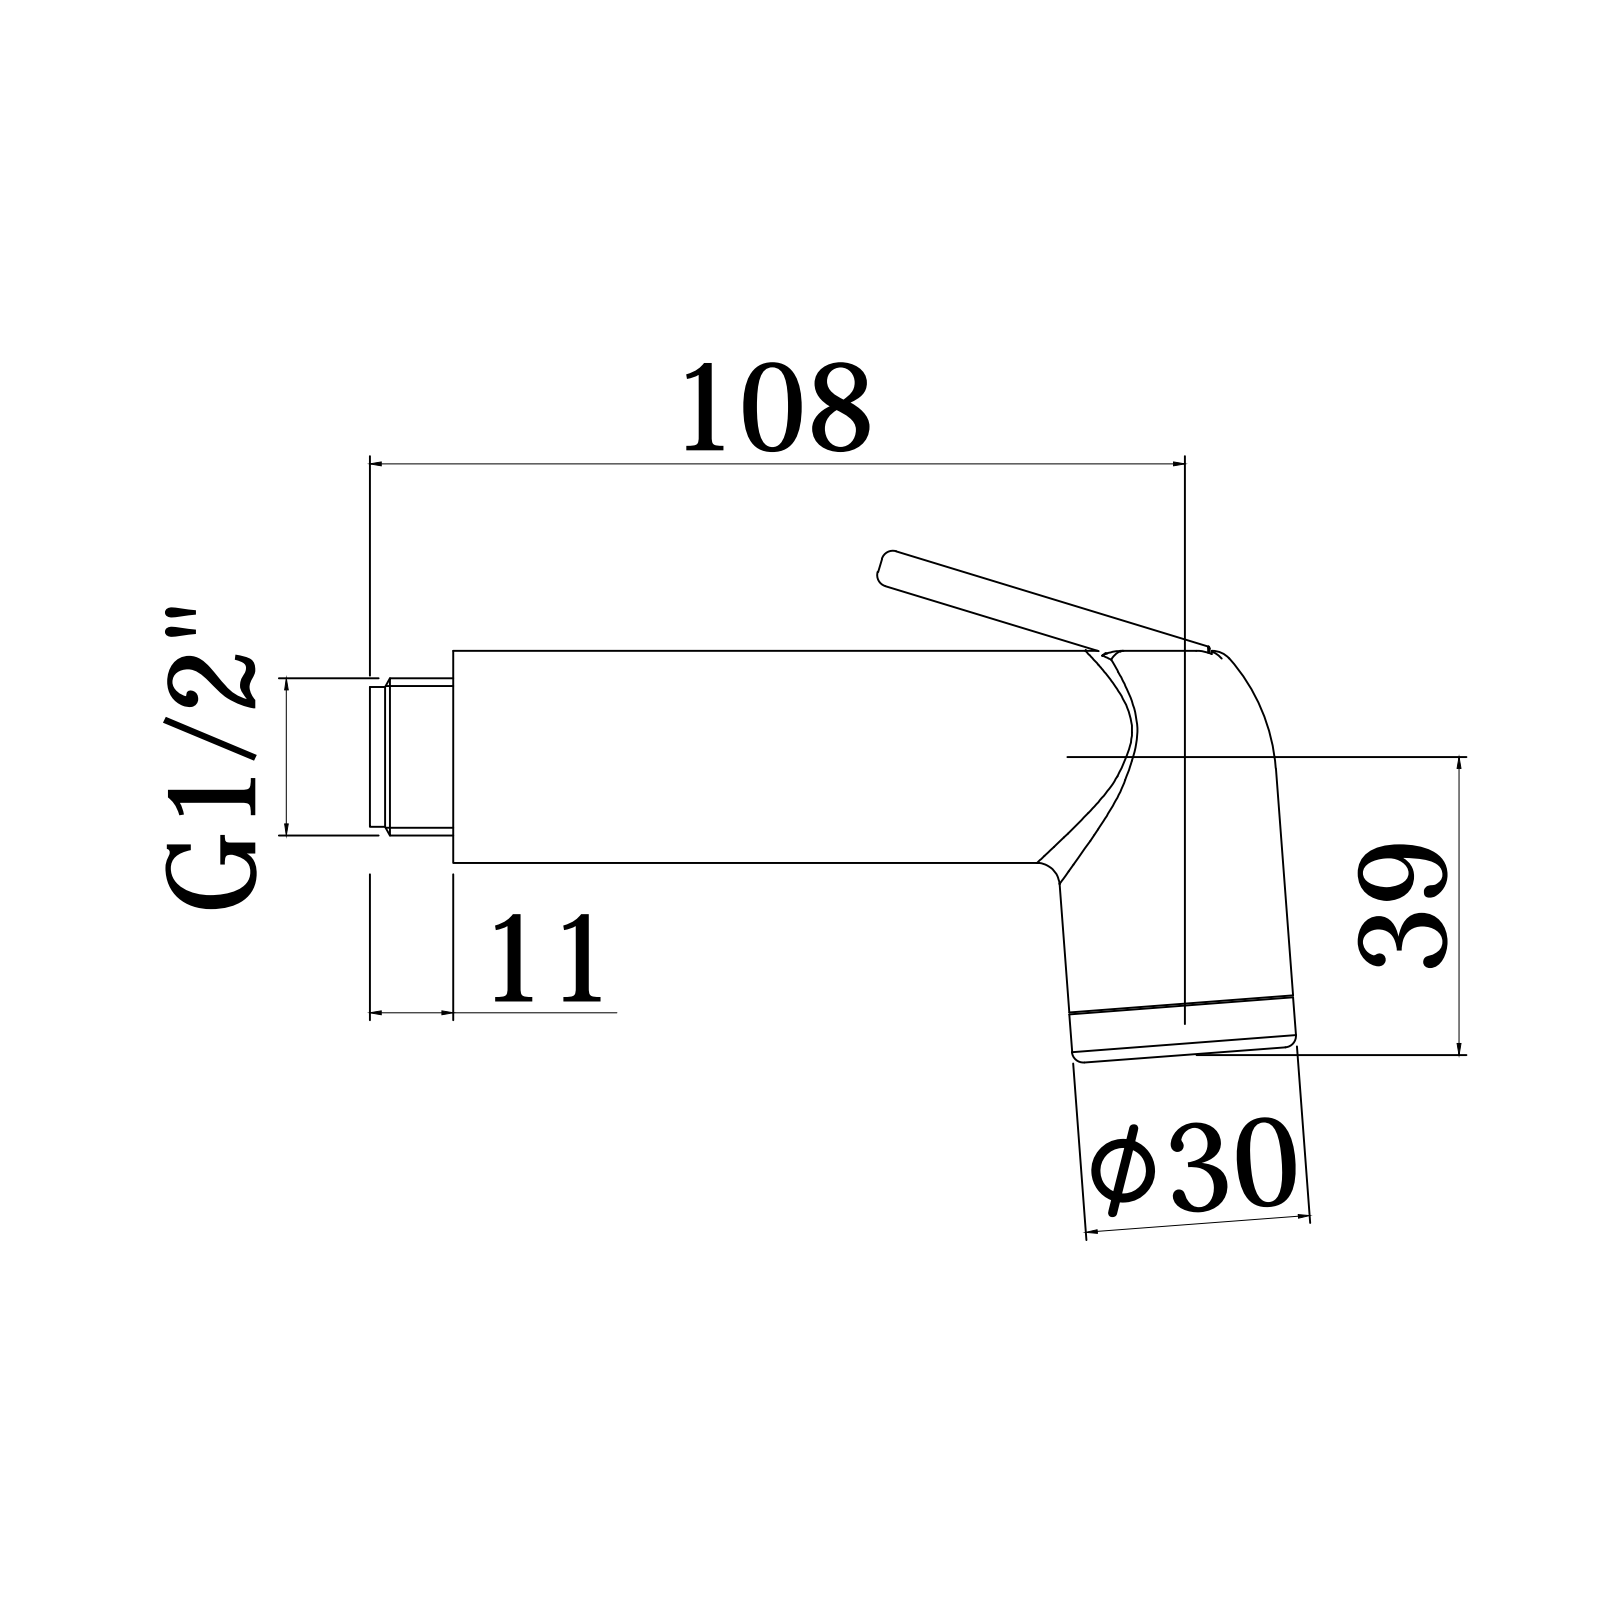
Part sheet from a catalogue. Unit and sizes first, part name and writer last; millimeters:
Units: millimetres
Overall size (bounding box): 120.43 × 75.37 × 28.8
Round holes (diameter × count): ⌀1.3 ×16, ⌀10.4 ×1, ⌀14.6 ×1, ⌀15.15 ×1, ⌀17.8 ×1, ⌀21.4 ×1
Round bosses / shafts (diameter × count): ⌀20.7 ×3, ⌀28.8 ×1, ⌀16.8 ×1, ⌀14.4 ×1, ⌀12.5 ×1, ⌀9.9 ×1, ⌀5.1 ×1, ⌀4.6 ×1
Partial cylindrical surfaces — rounded edges, fillets, slot ends (radius × count): R0.15 ×14, R1.6 ×6, R3 ×5, R0.5 ×4, R0.5 ×4, R0.9 ×4, R2 ×4, R1.49 ×3
Main face-to-face distances: 2, 3, 12, 14.8, 14.64, 41.98, 41.82, 27.18, 1.2, 1.04
Hole centre spacings: 10.16, 2.91, 2.92, 3.14, 4.1, 5.8, 6.02, 6.03
Bodies: 0 solids, 498 faces (86 planar, 191 cylindrical, 221 other)
Part name (STEP PRODUCT): ZDOC060CR
STEP written by: CREO PARAMETRIC BY PTC INC, 2020044 (CONFIG_CONTROL_DESIGN)
